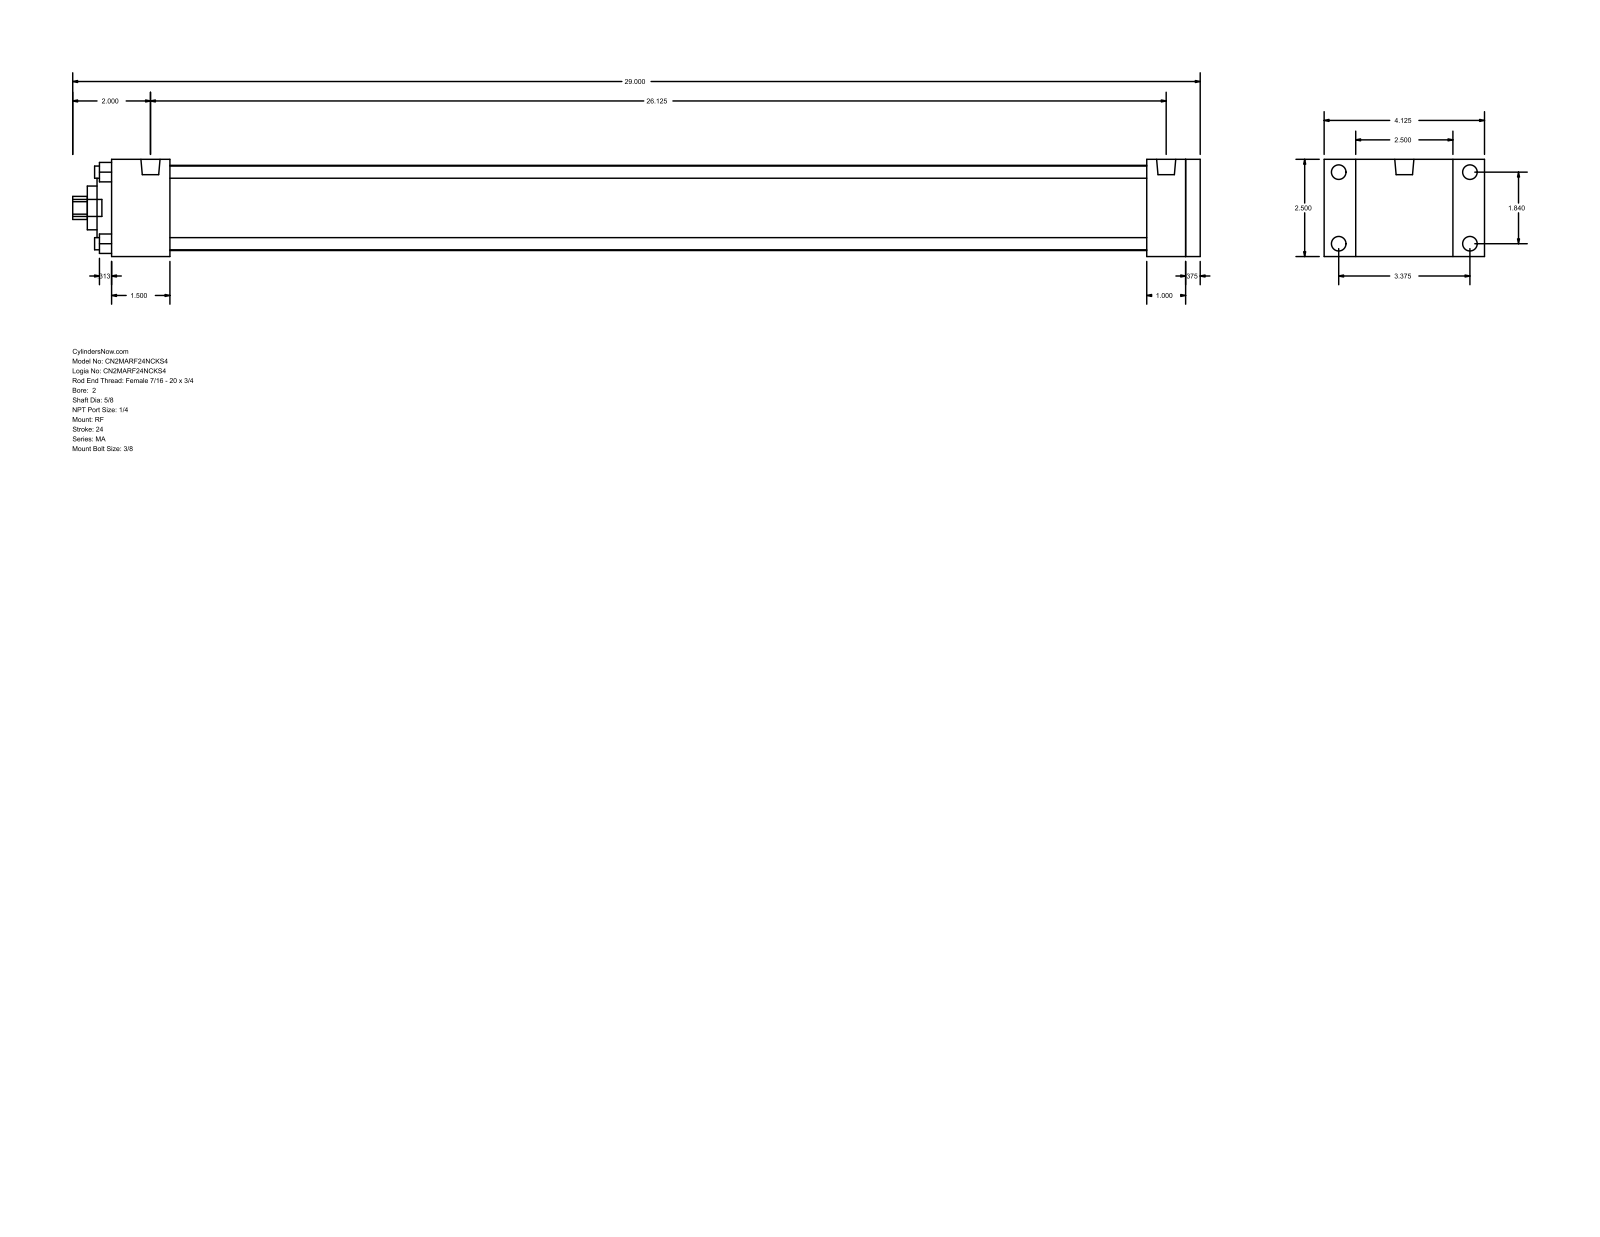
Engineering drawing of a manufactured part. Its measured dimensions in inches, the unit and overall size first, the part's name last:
Units: inches
Overall size (bounding box): 29 × 4.125 × 2.5
Round holes (diameter × count): ⌀0.313 ×4, ⌀0.625 ×1, ⌀1.125 ×1, ⌀2 ×1, ⌀2.19 ×1
Round bosses / shafts (diameter × count): ⌀0.375 ×4, ⌀0.313 ×4, ⌀0.492 ×2, ⌀0.437 ×1
Partial cylindrical surfaces — rounded edges, fillets, slot ends (radius × count): R0.297 ×1
Main face-to-face distances: 2.5, 0.375, 28, 1.5, 27.625, 26.125, 26.5, 26.625, 25.125, 1
Hole centre spacings: 1.301, 1.84, 2.602
Bodies: 0 solids, 94 faces (65 planar, 29 cylindrical, 0 other)
Part name (STEP PRODUCT): MA_RF__0200_0.625
STEP written by: GSSL Pune (CONFIG_CONTROL_DESIGN)
